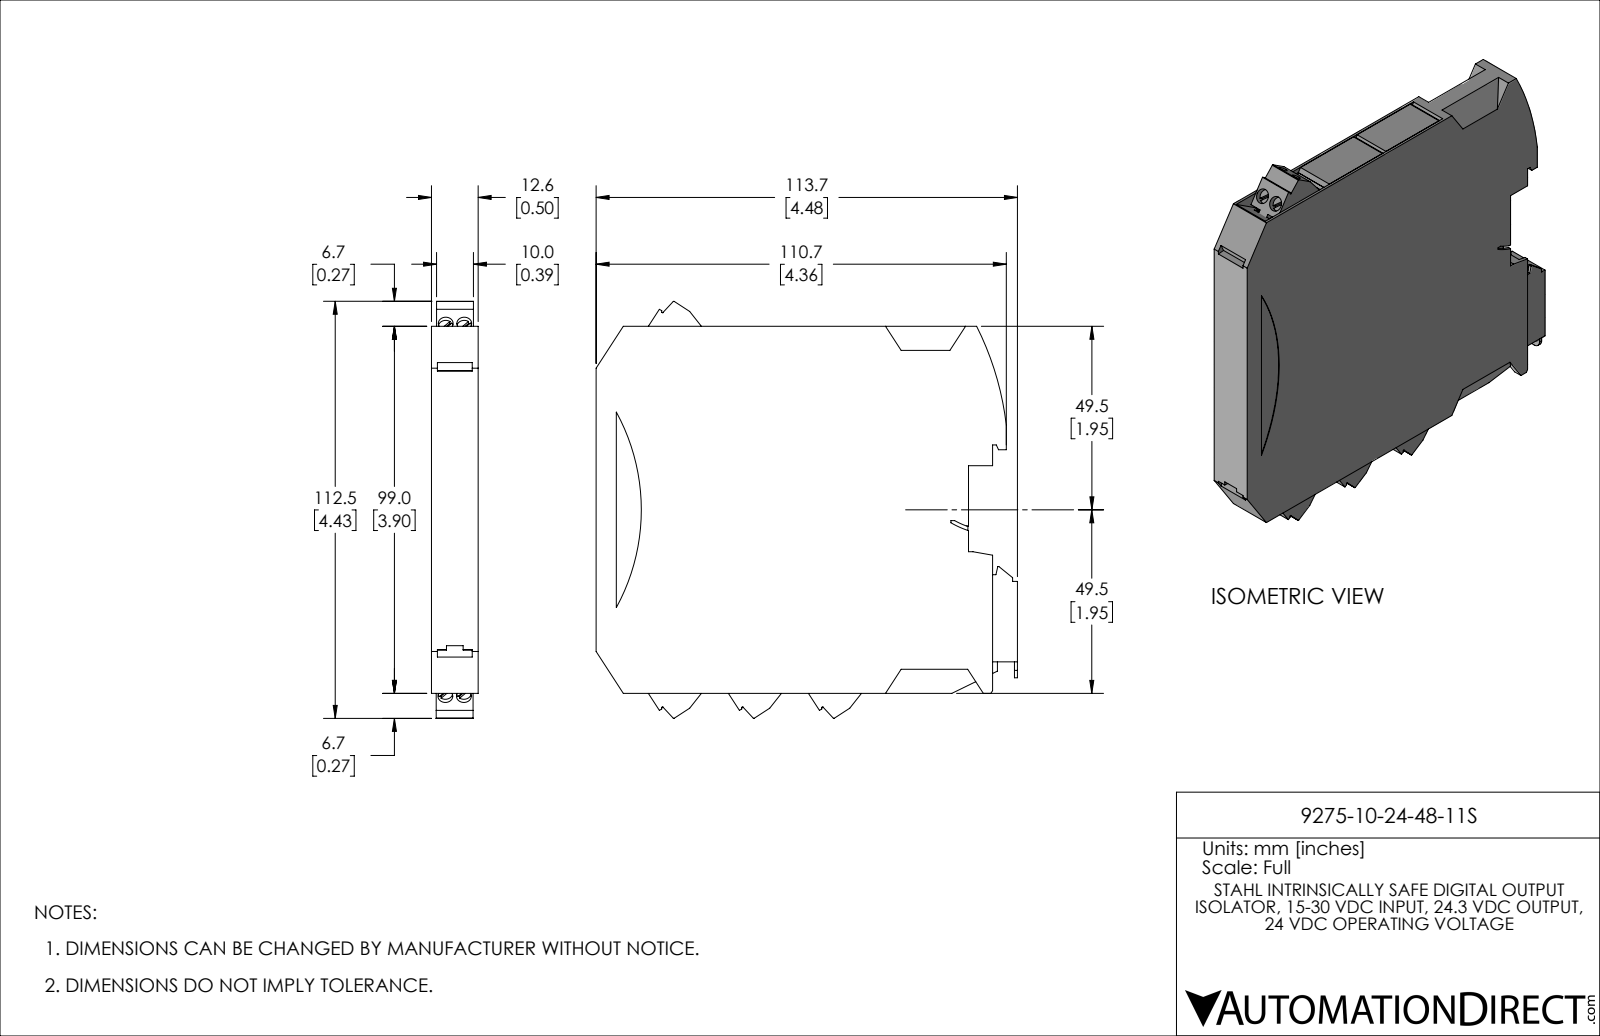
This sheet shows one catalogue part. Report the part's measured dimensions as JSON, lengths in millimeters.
{"part_name": "9275-10-24-48-11S", "step_written_by": "SolidWorks 2021 (AUTOMOTIVE_DESIGN)", "units": "millimeters", "bodies": {"solids": 7, "faces": 878, "planar": 785, "cylindrical": 85, "other": 8}, "overall_size": [113.7, 112.5, 12.6], "volume_mm3": 125800, "surface_area_mm2": 40950, "round_holes": [[1.5, 8], [2.2, 8], [3, 8], [4, 8]], "round_bosses_or_shafts": [[2.8, 6]], "partial_cylinders_radius": [[3, 14], [2.9, 8], [1.4, 6], [0.2, 4], [0.5, 2], [1.5, 2], [2, 2], [2.5, 2]], "face_to_face_distances": [12.6, 0.8, 11.9, 18.1, 10, 11.8, 11.1, 1.3, 11.3, 0.5], "hole_center_spacings": [5, 18.1, 11.8, 18.8, 21.6, 22.1, 12.8, 12.8]}
